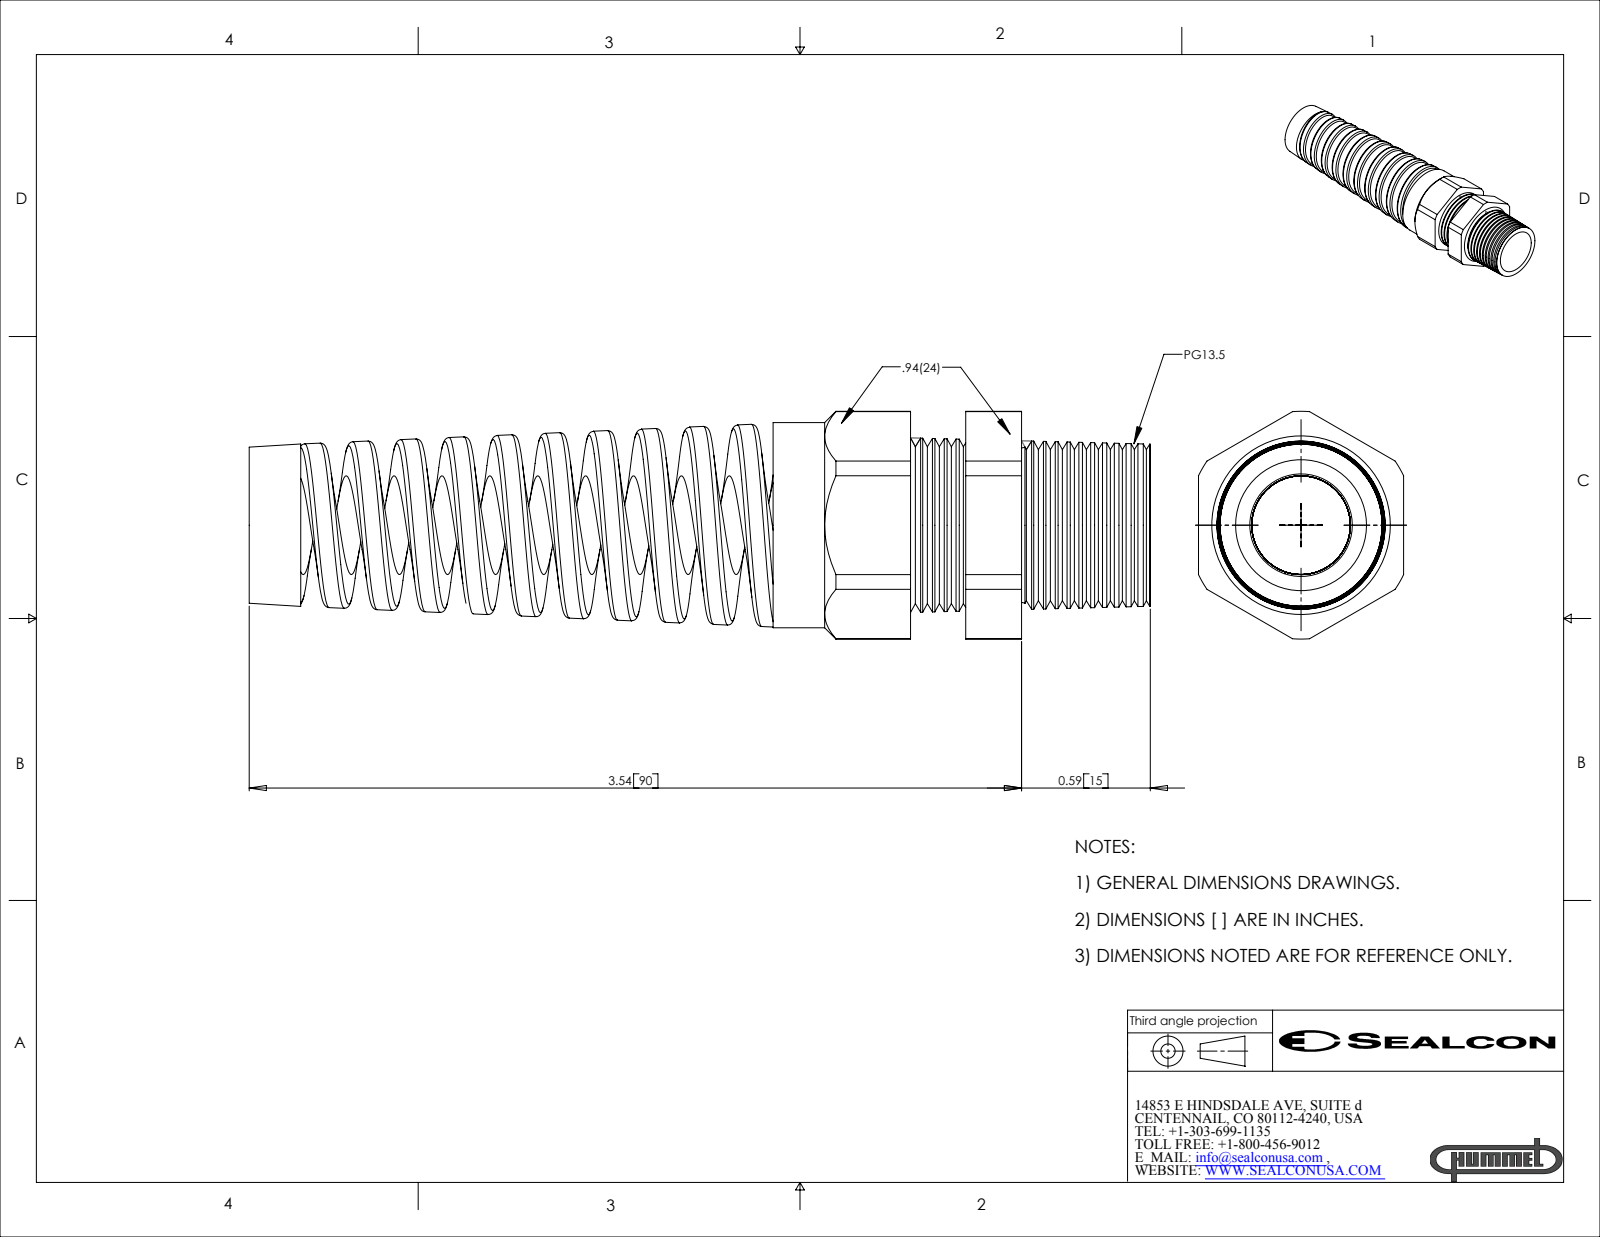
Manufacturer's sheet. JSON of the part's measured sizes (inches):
{"part_name": "CF13CA-GY", "step_written_by": "SolidWorks 2007 (CONFIG_CONTROL_DESIGN)", "units": "inches", "bodies": {"solids": 2, "faces": 209, "planar": 24, "cylindrical": 46, "other": 139}, "overall_size": [4.13, 1.043, 0.94], "volume_in3": 1.191, "surface_area_in2": 24.35, "round_holes": [[0.453, 1], [0.47, 1], [0.482, 1]], "round_bosses_or_shafts": [[0.94, 1], [0.6, 1]], "partial_cylinders_radius": [[0.522, 1]], "face_to_face_distances": [0.94, 2.401, 0.253, 0.236, 0.63, 0.883, 1.139, 0.509, 0.256, 3.031]}
